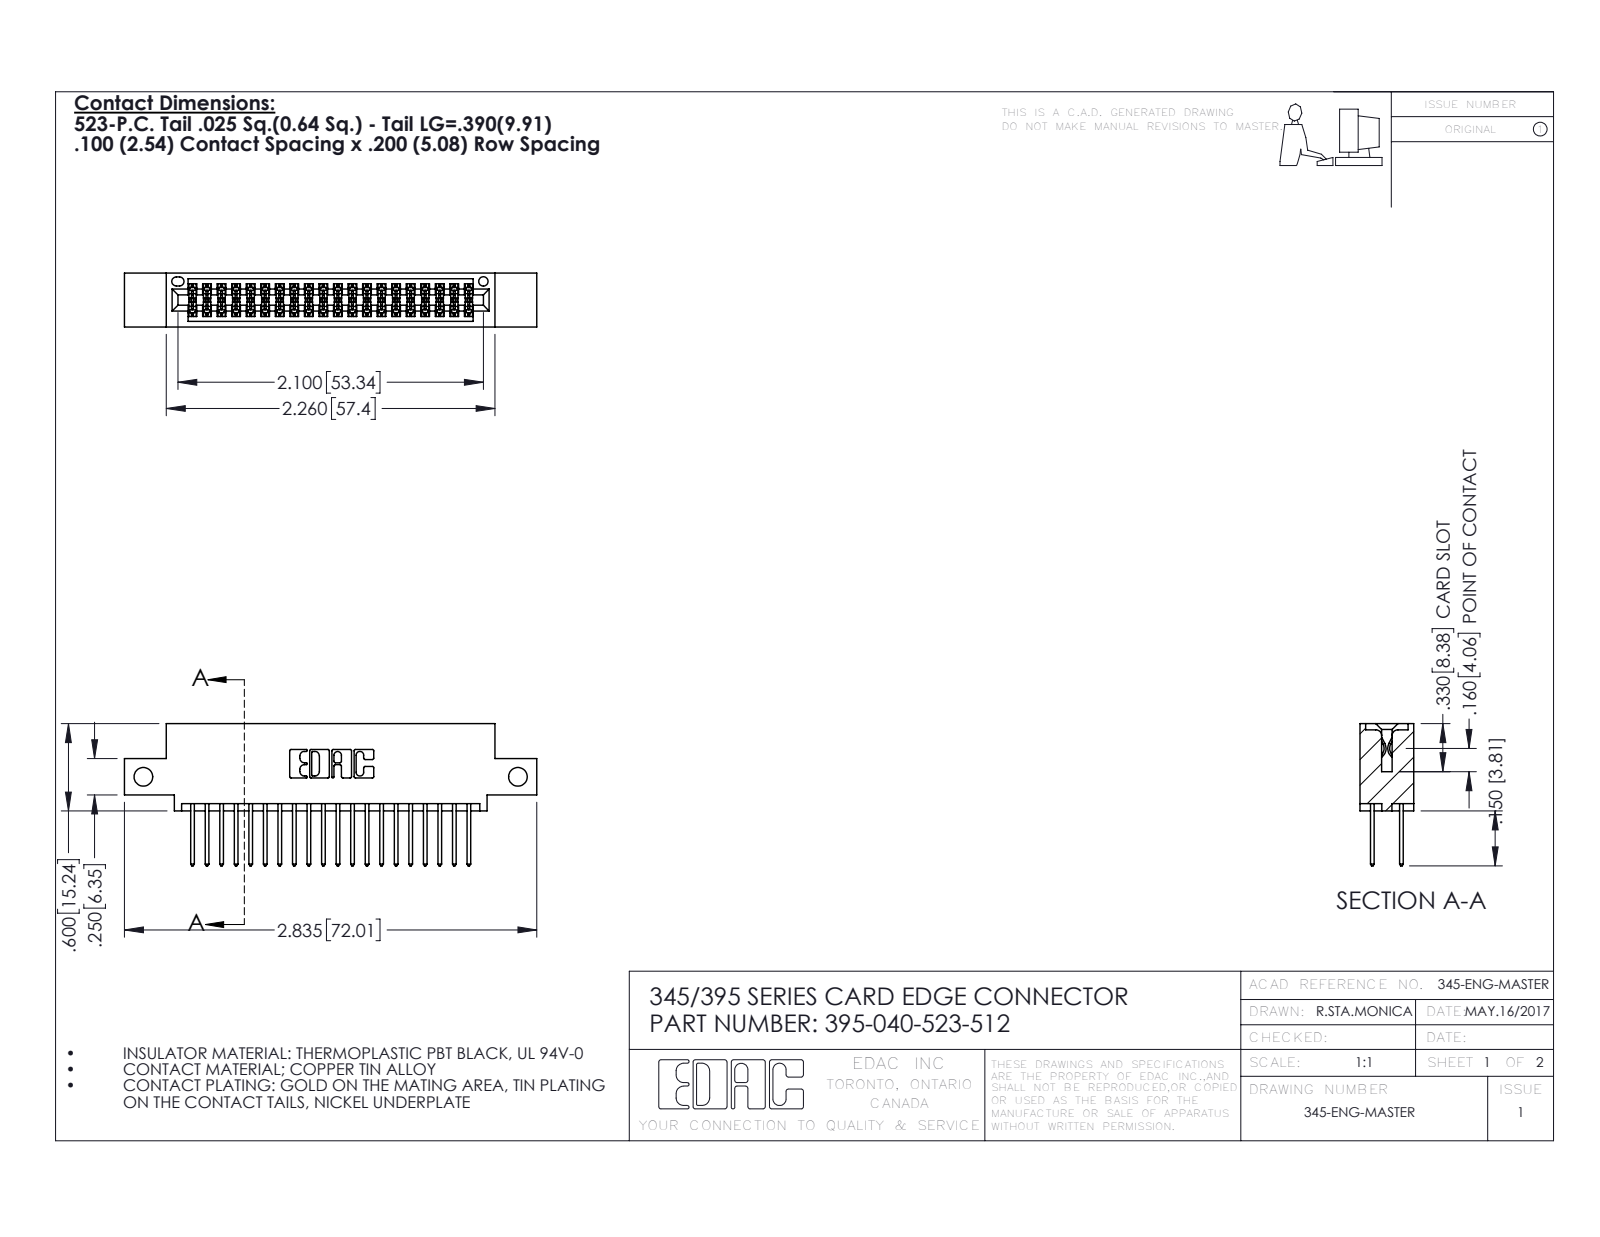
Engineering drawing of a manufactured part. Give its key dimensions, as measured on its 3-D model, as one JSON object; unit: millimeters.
{"part_name": "345-292-001_345-293-123; 395-040-523-512; 345 Part_0.110 Offset - Side Mount", "step_written_by": "SolidWorks 2016 (CONFIG_CONTROL_DESIGN)", "units": "millimeters", "bodies": {"solids": 41, "faces": 2130, "planar": 1404, "cylindrical": 726, "other": 0}, "overall_size": [72, 24.8, 9.4], "volume_mm3": 6720, "surface_area_mm2": 9819, "round_holes": [[3.3, 2], [1.6, 1]], "partial_cylinders_radius": [[0.2, 60], [0.3, 40], [0.3, 22], [0.2, 6], [0.8, 6], [0.7, 3], [0.4, 2], [0.5, 2]], "face_to_face_distances": [7.6, 1.8, 5.1, 2.5, 6.9, 0.6, 9.4, 5.7, 4.4, 3.8], "hole_center_spacings": [65.4]}
